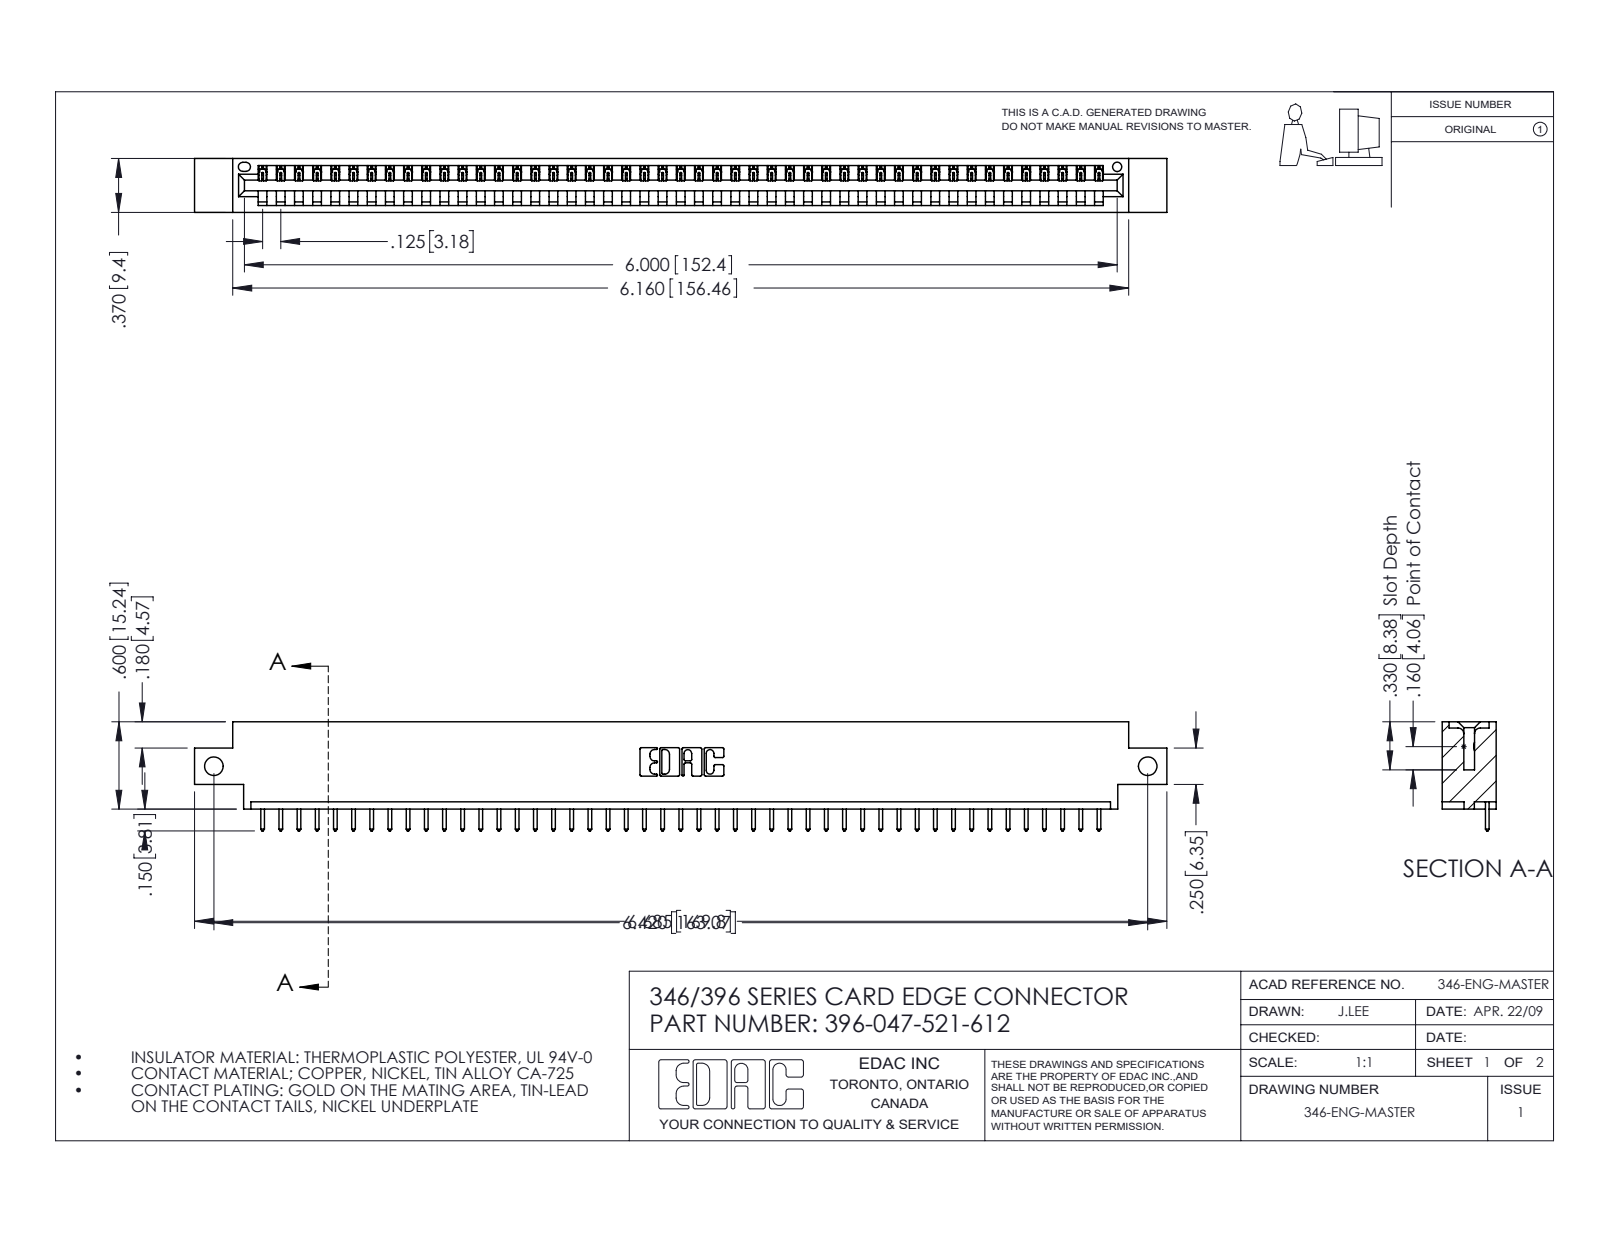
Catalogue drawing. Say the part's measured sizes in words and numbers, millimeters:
The part is named "346 Part_0.170 Offset - Side Mount; 396-047-521-612; 345-292-001_345-293-121". Its 3-D file was written by "SolidWorks 2016 (CONFIG_CONTROL_DESIGN)". It is 48 solids with 2852 faces: 1960 planar, 892 cylindrical and 0 other. Overall it measures 169.8 by 19.1 by 9.4 millimeters. Its volume is 15 900 cubic millimeters and its surface area 19 430 square millimeters. Round holes: 2 of diameter 3.3, 1 of diameter 1.6. Partial cylindrical surfaces (rounded edges, fillets, slot ends): 94 of radius 0.2, 94 of radius 0.3, 22 of radius 0.3, 6 of radius 0.2, 6 of radius 0.8, 3 of radius 0.7, 2 of radius 0.8, 2 of radius 1. The main face-to-face distances are 1.2, 8.2, 9.4, 6.4, 1.8, 7.6, 0.6, 3.8, 5.6, 2.5. The hole center spacings are 163.1.
